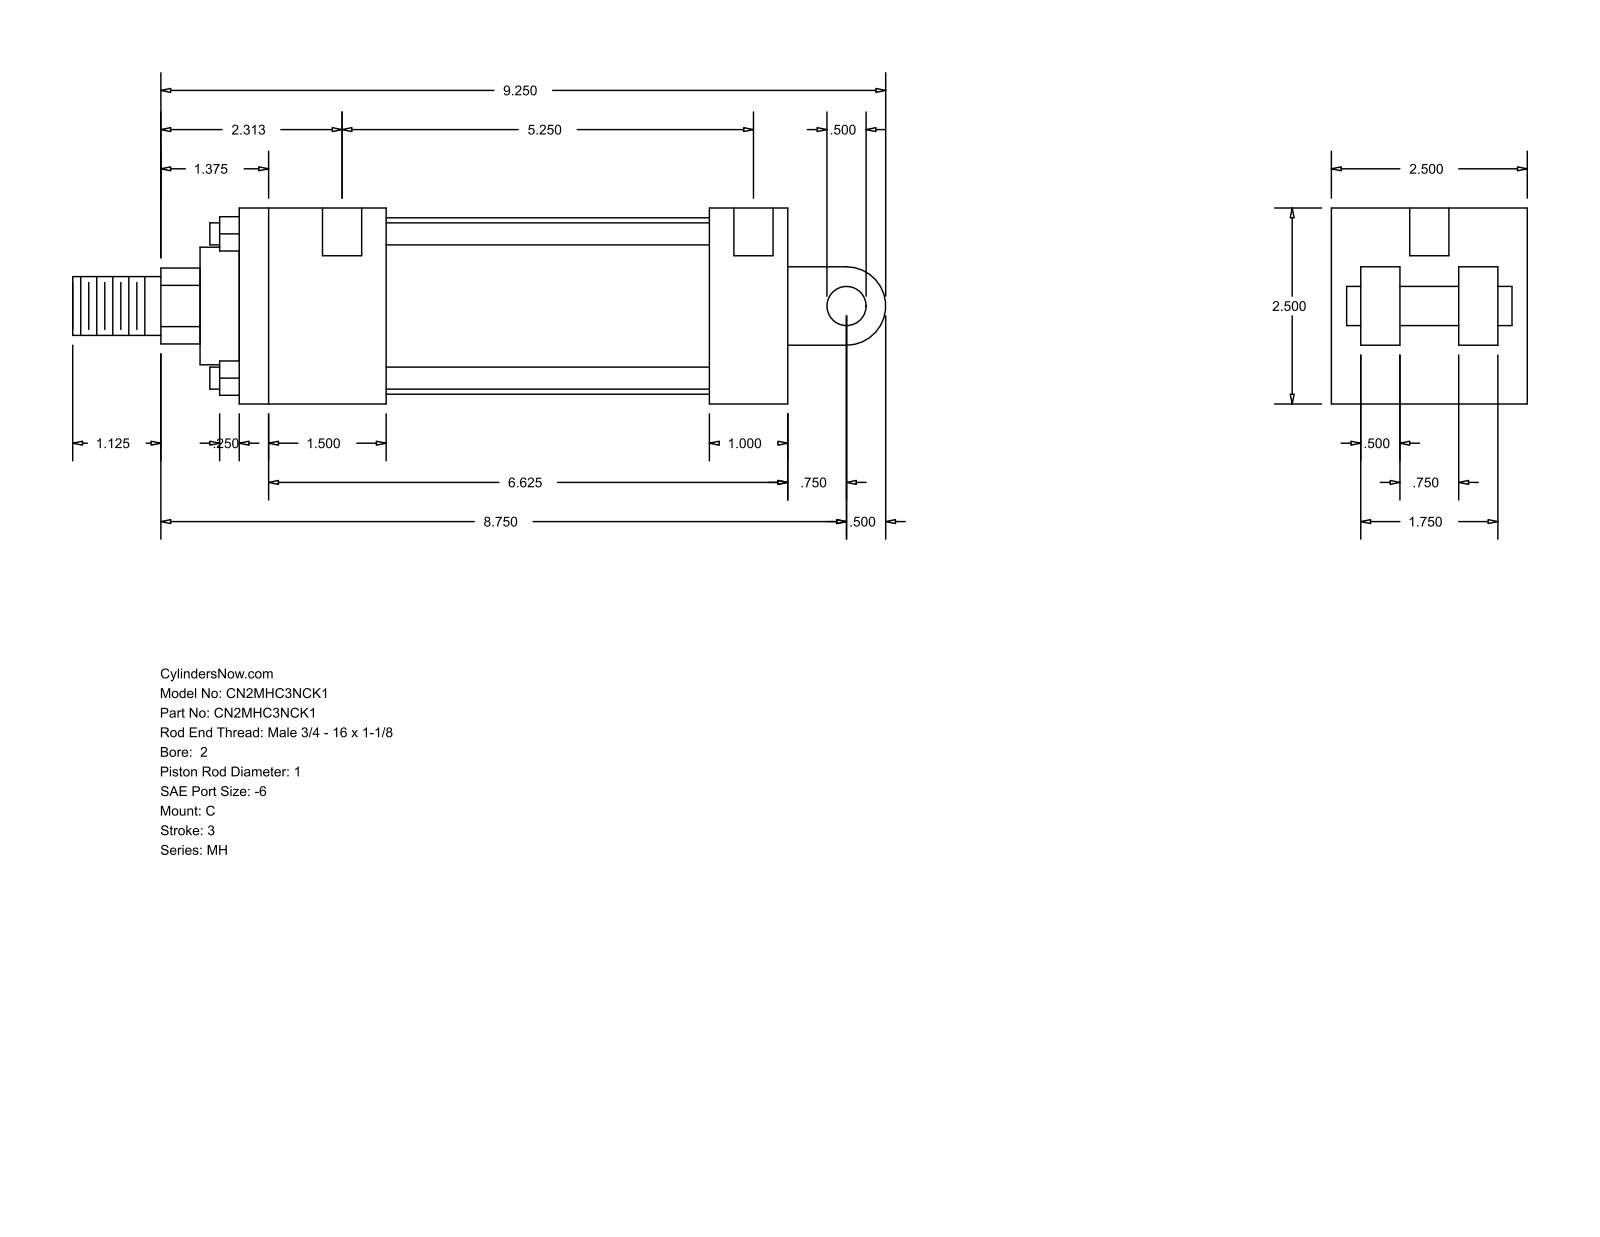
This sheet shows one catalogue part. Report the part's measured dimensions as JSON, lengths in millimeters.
{"part_name": "MH_C__0200_1", "step_written_by": "GSSL Pune (CONFIG_CONTROL_DESIGN)", "units": "millimeters", "bodies": {"solids": 0, "faces": 99, "planar": 70, "cylindrical": 29, "other": 0}, "overall_size": [263.52, 63.5, 63.5], "round_holes": [[5.56, 4], [12.7, 2]], "round_bosses_or_shafts": [[7.14, 4], [57.15, 1], [38.1, 1], [25.4, 1], [19.05, 1], [12.7, 1]], "partial_cylinders_radius": [[12.29, 1], [12.7, 1]], "face_to_face_distances": [63.5, 177.8, 12.7, 25.4, 47.63, 53.98, 9.52, 152.4, 104.77, 130.17], "hole_center_spacings": [141.28, 3.17, 4.76, 133.35, 136.52, 138.11]}
